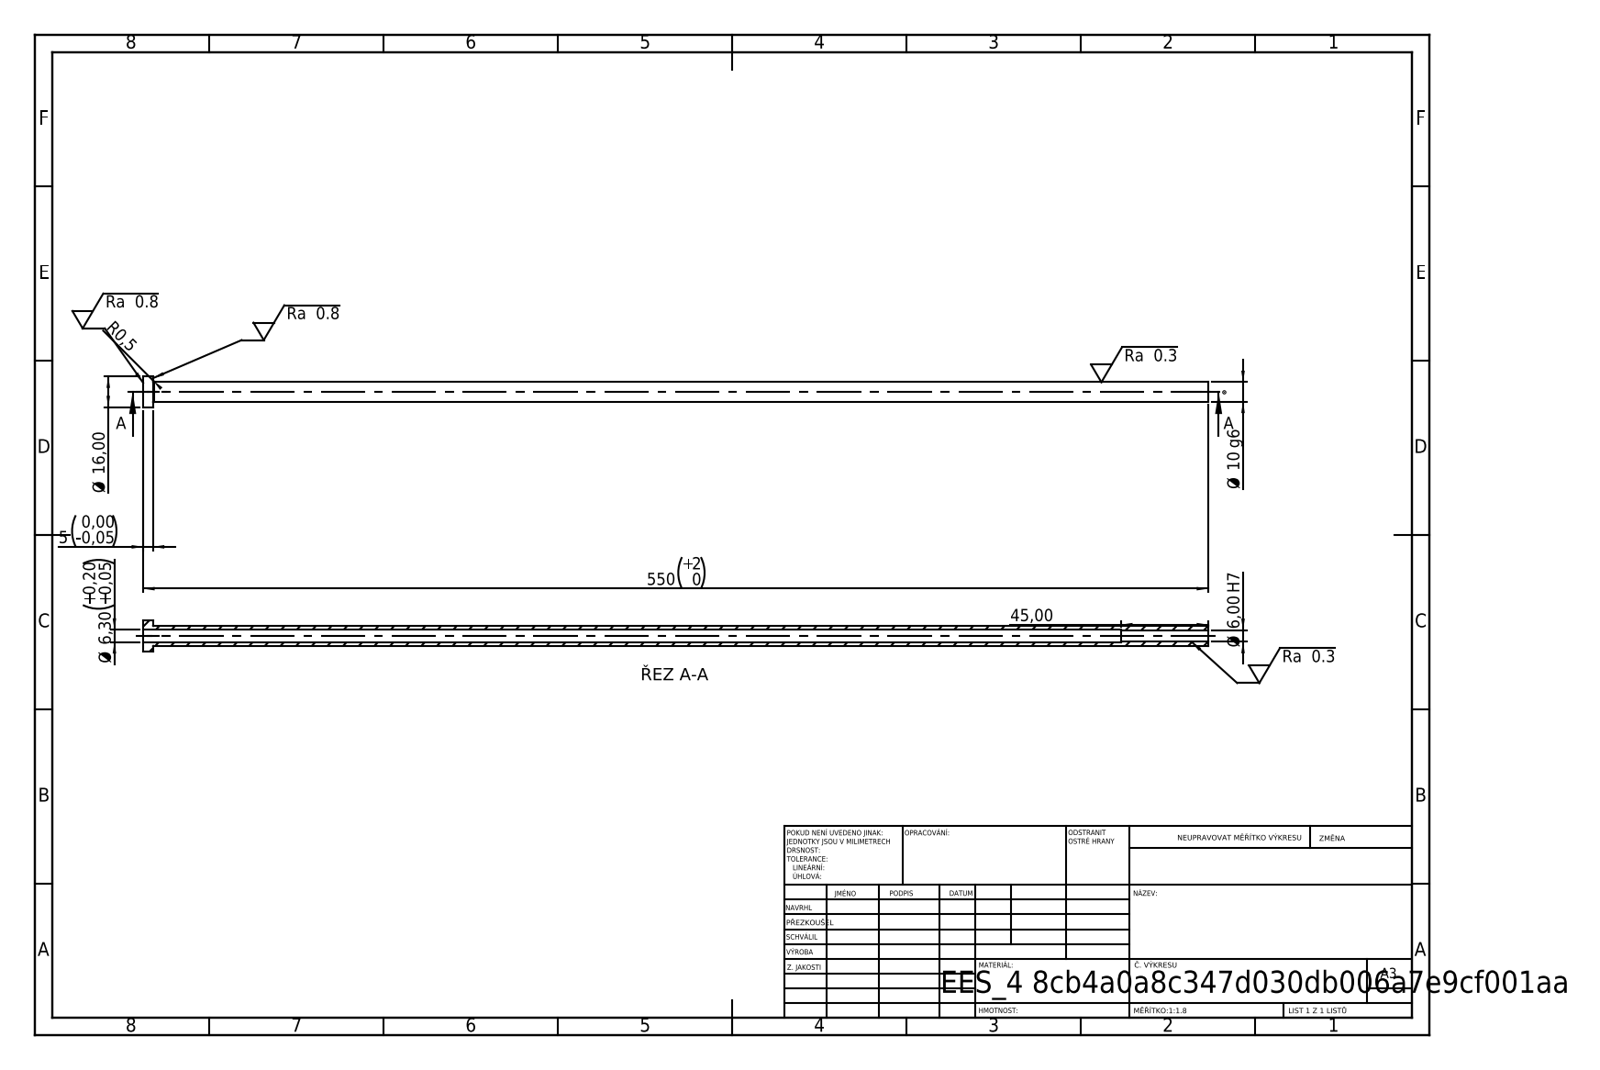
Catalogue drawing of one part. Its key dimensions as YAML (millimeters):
step_written_by: "SolidWorks 2019 (CONFIG_CONTROL_DESIGN)"
units: millimeters
bodies: {solids: 1, faces: 14, planar: 4, cylindrical: 8, other: 2}
overall_size: [550, 16, 16]
volume: 26797
surface_area: 28555
round_holes:
  - {diameter: 6, count: 1}
  - {diameter: 6.3, count: 1}
round_bosses_or_shafts:
  - {diameter: 16, count: 1}
  - {diameter: 10, count: 1}
face_to_face_distances: [5, 550, 545, 505, 500, 45]
